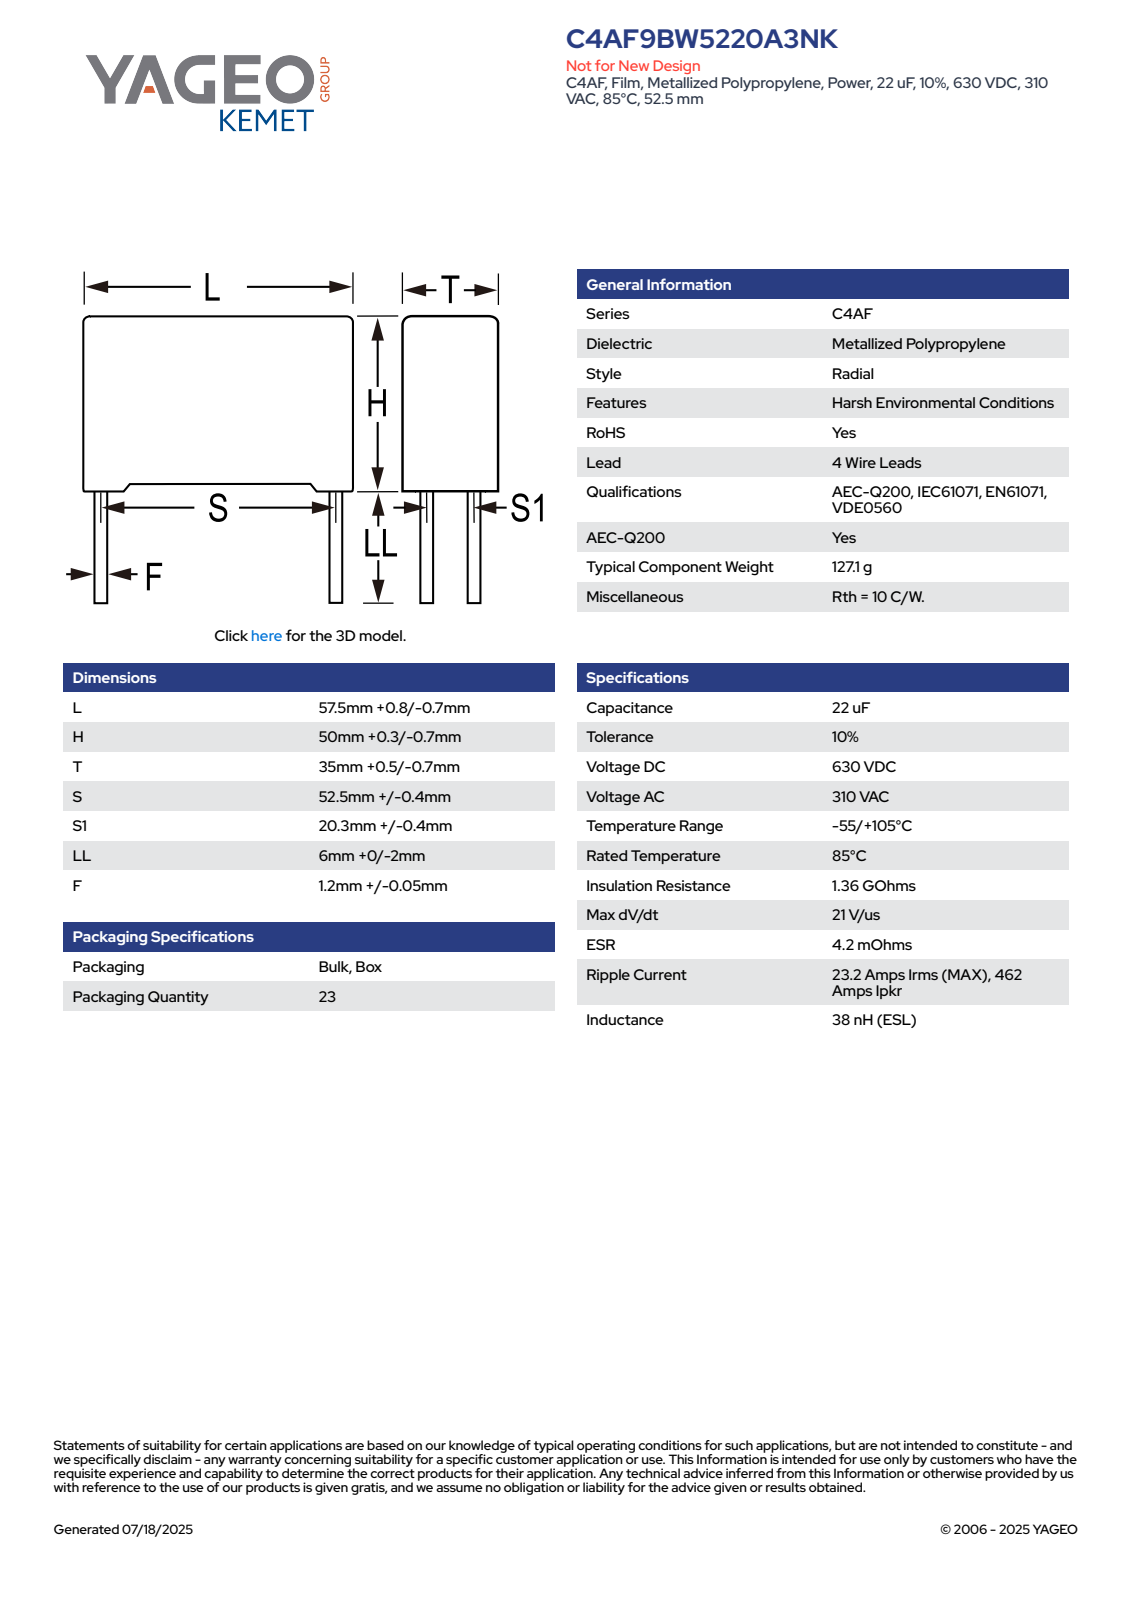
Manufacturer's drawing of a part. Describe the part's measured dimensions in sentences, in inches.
The part is named "CFP_RB4_57.5X50X35_L58.3H50.3T35.5S52.5S120.3LL6F1.25". Its 3-D file was written by "SolidWorks 2014 (AUTOMOTIVE_DESIGN)". It is 4 solids with 87 faces: 79 planar, 8 cylindrical and 0 other. Overall it measures 2.295 by 2.217 by 1.398 inches. Its volume is 6.187 cubic inches and its surface area 21.57 square inches. Round bosses or shafts: 4 of diameter 0.049. The main face-to-face distances are 1.398, 1.922, 2.295, 0.058, 1.98, 0.086, 2.209, 2.124, 1.312, 1.226.
